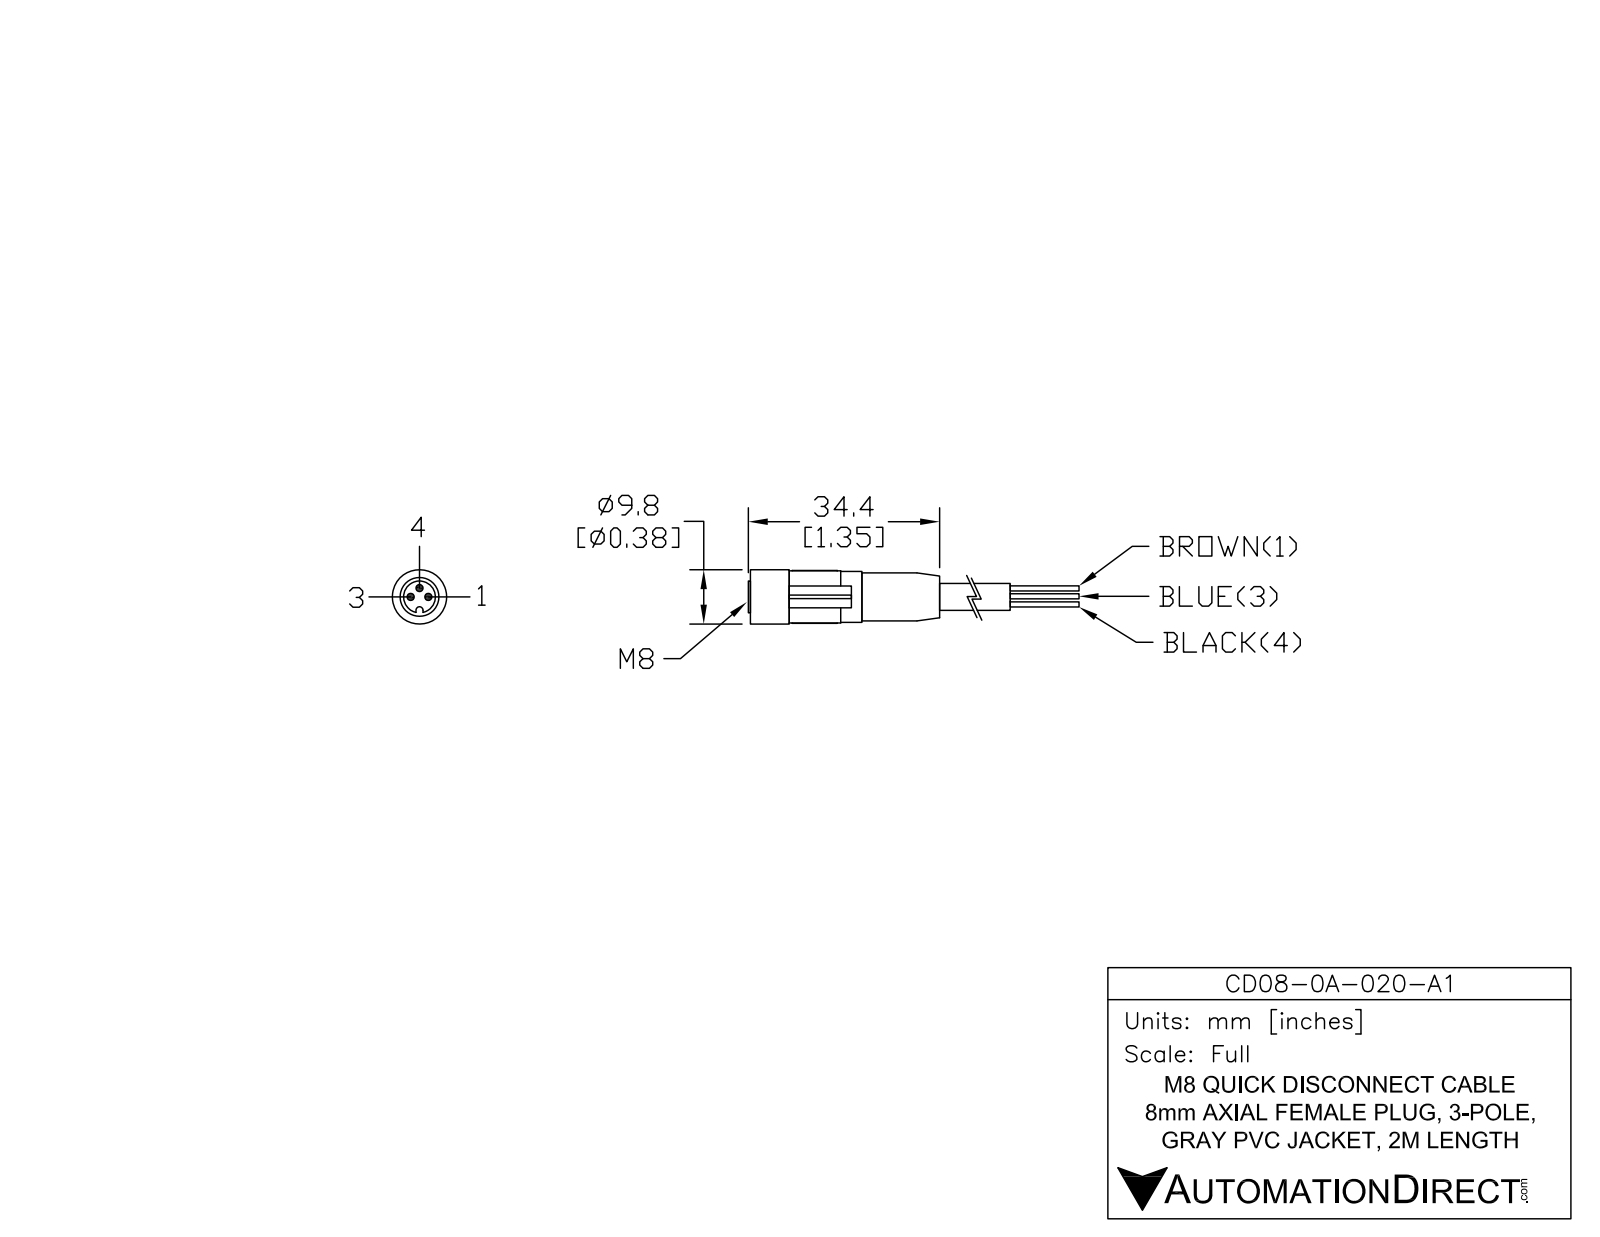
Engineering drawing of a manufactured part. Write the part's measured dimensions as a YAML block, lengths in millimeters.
part_name: "CD08-0A-020-A1"
step_written_by: "SolidWorks 2017 (AUTOMOTIVE_DESIGN)"
units: millimeters
bodies: {solids: 4, faces: 304, planar: 222, cylindrical: 78, other: 4}
overall_size: [134.6, 10, 10]
volume: 4158
surface_area: 3249
round_holes:
  - {diameter: 0.9, count: 3}
  - {diameter: 5.6, count: 1}
  - {diameter: 8, count: 1}
round_bosses_or_shafts:
  - {diameter: 10, count: 1}
  - {diameter: 5.5, count: 1}
  - {diameter: 4.8, count: 1}
partial_cylinders:
  - {radius: 0.5, count: 1}
  - {radius: 4.9, count: 1}
face_to_face_distances: [26.9, 9, 0.6, 4.6, 30, 3.1, 4, 34, 7.1, 34.6]
hole_center_spacings: [1.6, 2.26, 3.2]
